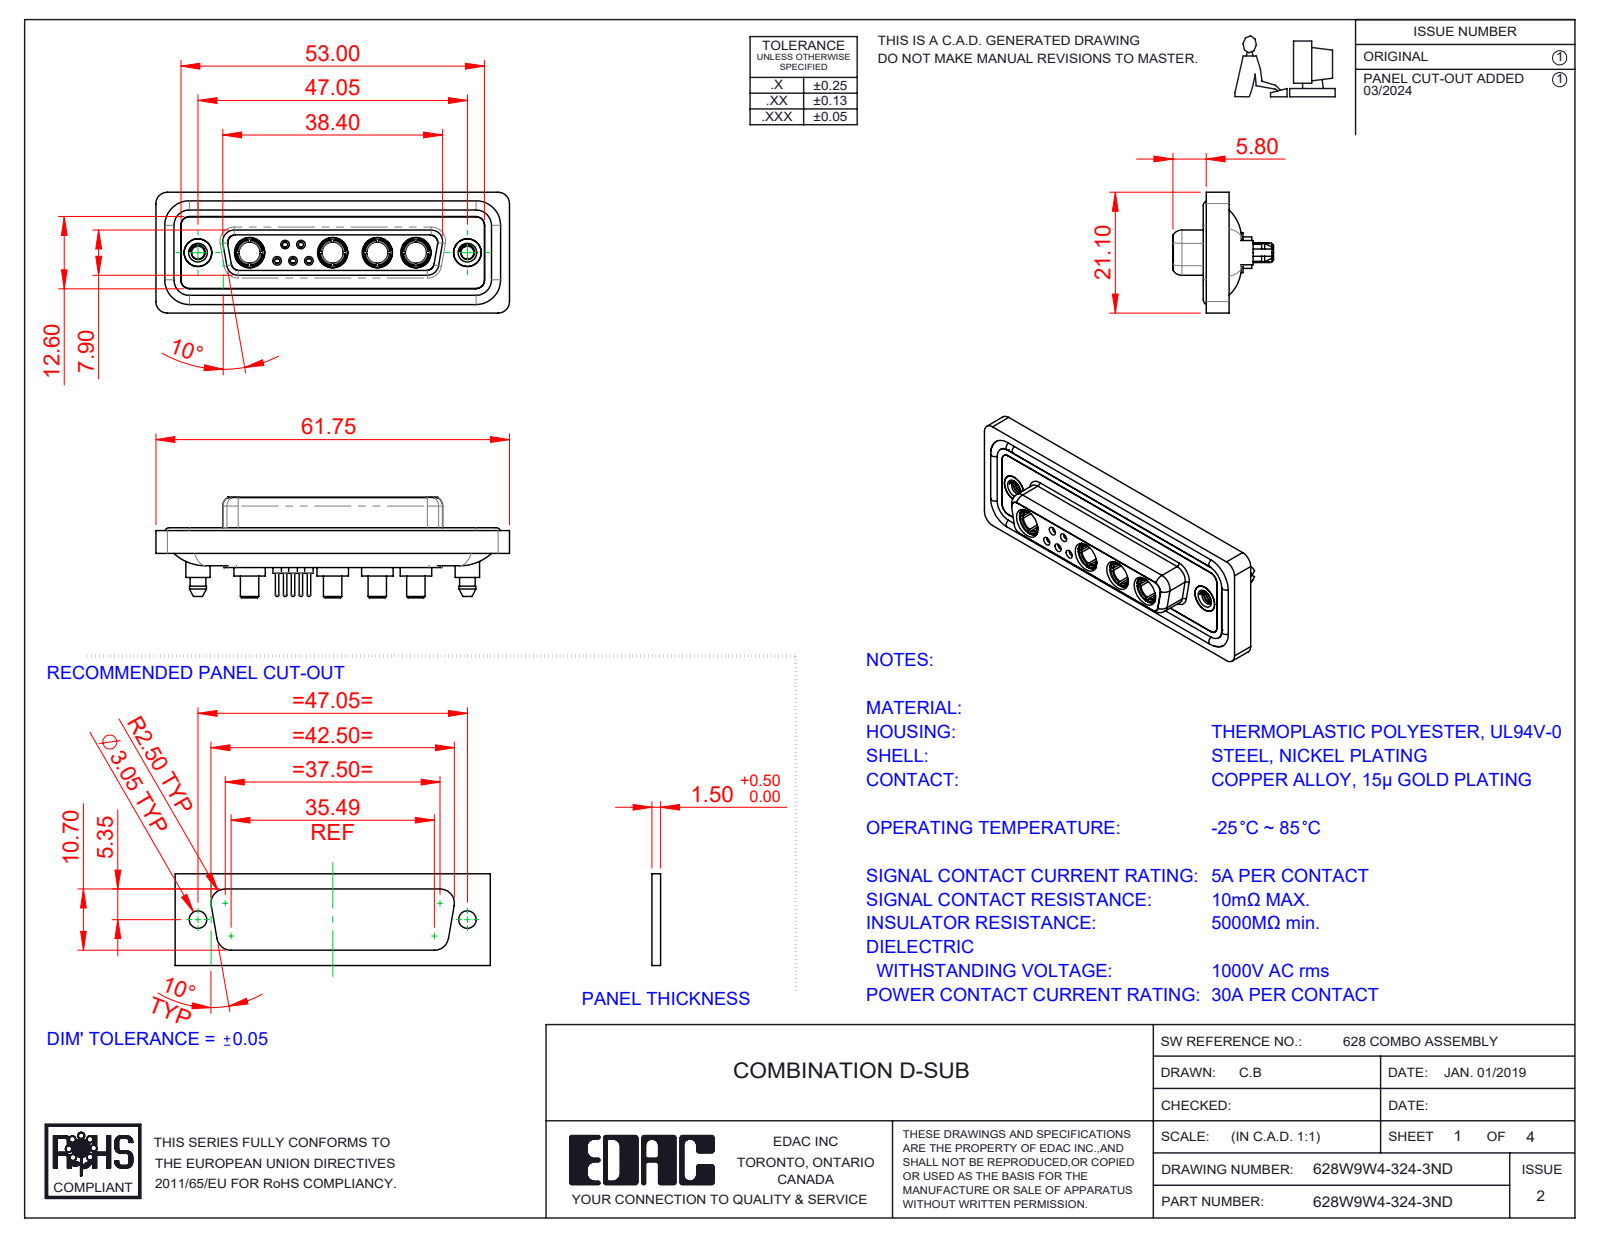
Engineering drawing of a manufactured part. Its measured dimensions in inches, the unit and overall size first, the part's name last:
Units: inches
Overall size (bounding box): 2.431 × 0.831 × 0.691
Round holes (diameter × count): ⌀0.191 ×6, ⌀0.035 ×5, ⌀0.043 ×5, ⌀0.059 ×5, ⌀0.079 ×5, ⌀0.146 ×4, ⌀0.209 ×4, ⌀0.063 ×3, ⌀0.067 ×2, ⌀0.089 ×2, ⌀0.157 ×2, ⌀0.159 ×2
Round bosses / shafts (diameter × count): ⌀0.063 ×6, ⌀0.087 ×5, ⌀0.024 ×5, ⌀0.217 ×4, ⌀0.205 ×4, ⌀0.195 ×4, ⌀0.187 ×4, ⌀0.148 ×4
Partial cylindrical surfaces — rounded edges, fillets, slot ends (radius × count): R0.059 ×24, R0.079 ×18, R0.063 ×10, R0.053 ×8, R0.01 ×4, R0.02 ×4, R0.024 ×4, R0.026 ×4
Main face-to-face distances: 0.016, 0.071, 0.293, 0.222, 0.02, 0.278, 0.26, 0.063, 0.043, 0.114
Hole centre spacings: 0.124, 0.109, 0.198, 0.109, 0.173, 0.198, 0.218, 0.226
Volume: 0.512 in³ · Surface area: 21.58 in²
Bodies: 20 solids, 1023 faces (312 planar, 423 cylindrical, 288 other)
Part name (STEP PRODUCT): 628Combo Threaded Boardlock_D; 628Combo Contact Row 2_24; 628Combo Waterproof Housing_25 Contacts; 628Combo Shell Front_25 Contacts (+5 more)
STEP written by: SolidWorks 2023 (CONFIG_CONTROL_DESIGN)
